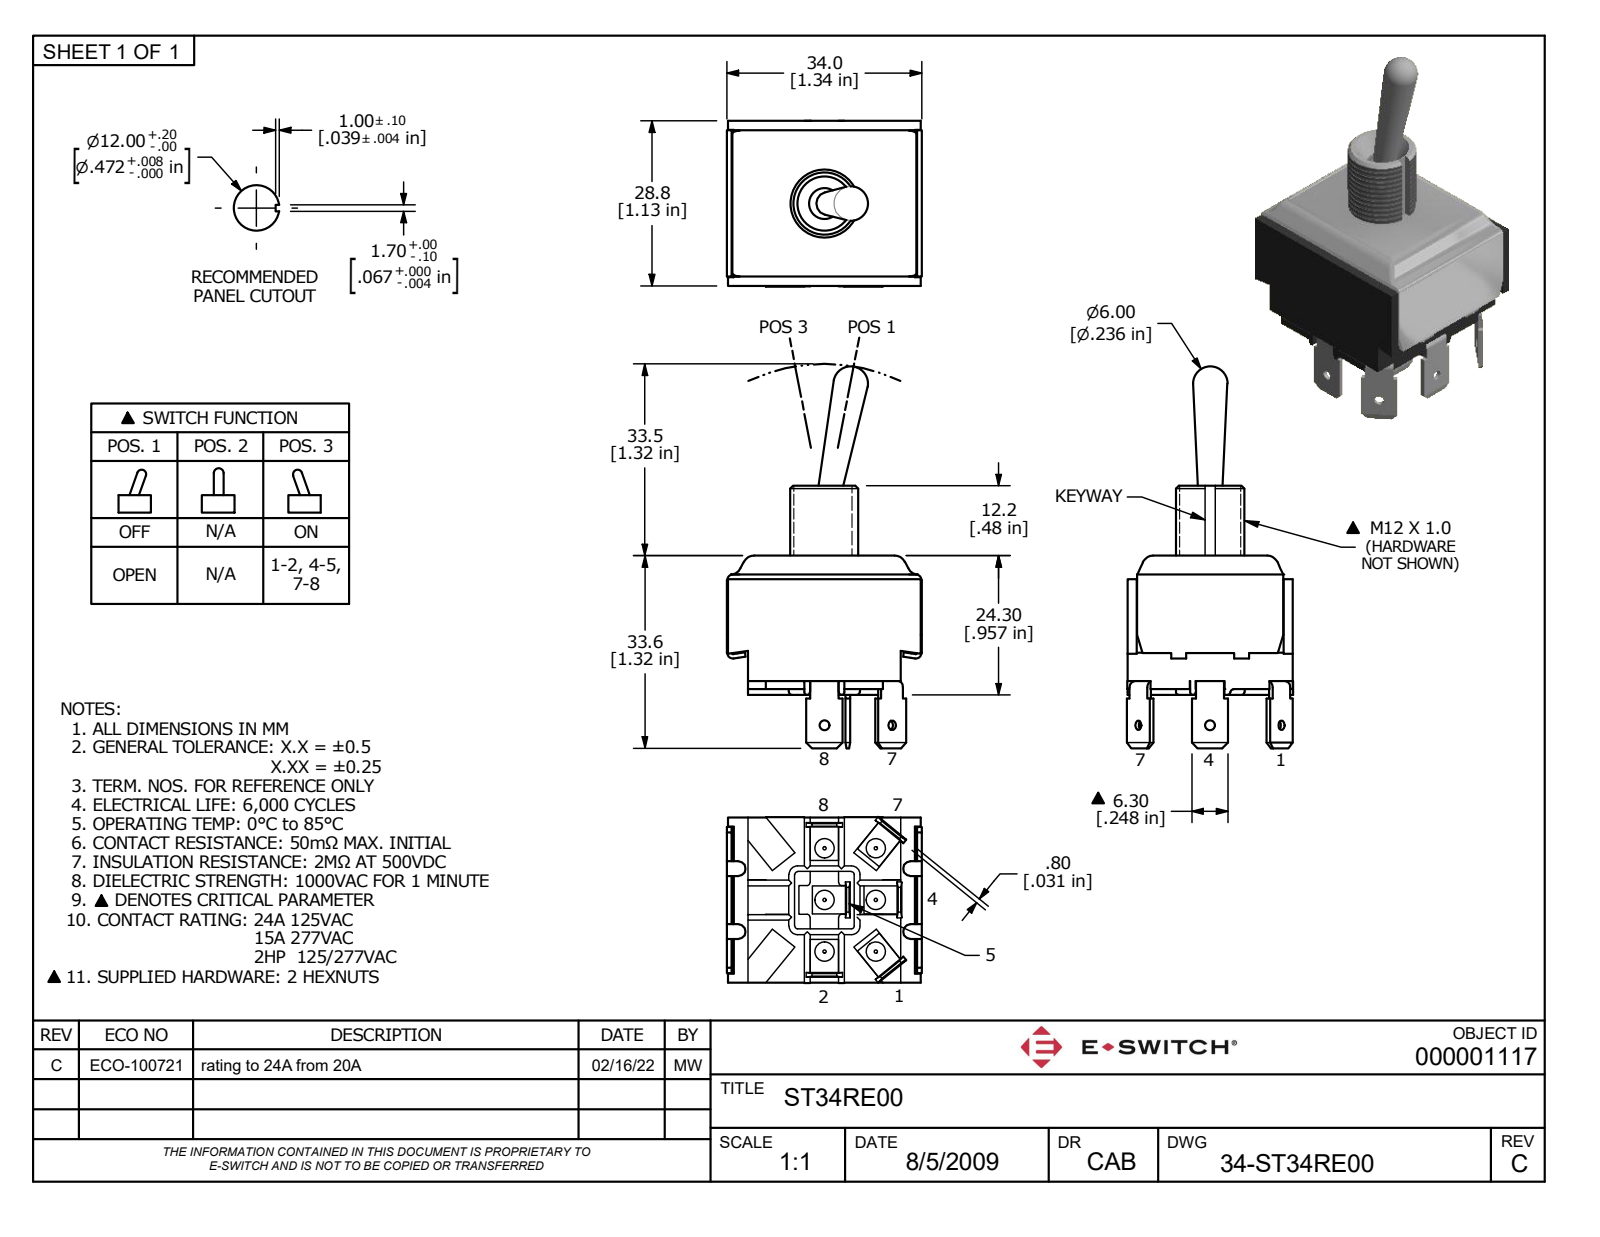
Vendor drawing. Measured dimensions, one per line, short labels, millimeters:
name: ST34RE00
written by: Autodesk Inventor 2020 (AUTOMOTIVE_DESIGN)
unit: mm
bodies: 1 solid, 489 faces (332 planar, 90 cylindrical, 67 other)
size: 66.66 × 34 × 28.98
volume: 21 927 mm³; area: 9 089 mm²
holes: 9× ⌀2, 6× ⌀1.8, 1× ⌀5.4
bosses: 1× ⌀11.91
rounds: 17× R0.5, 9× R0.3, 9× R1.1, 6× R2, 4× R0.2, 4× R0.8, 4× R1, 4× R1.3
face distances: 0.8, 1.2, 0.4, 32, 32.8, 33.2, 28.8, 3.65, 30.35, 2.85
hole spacings: 9, 12.73, 20.12, 18, 2.66, 12.69, 12.76, 25.46
